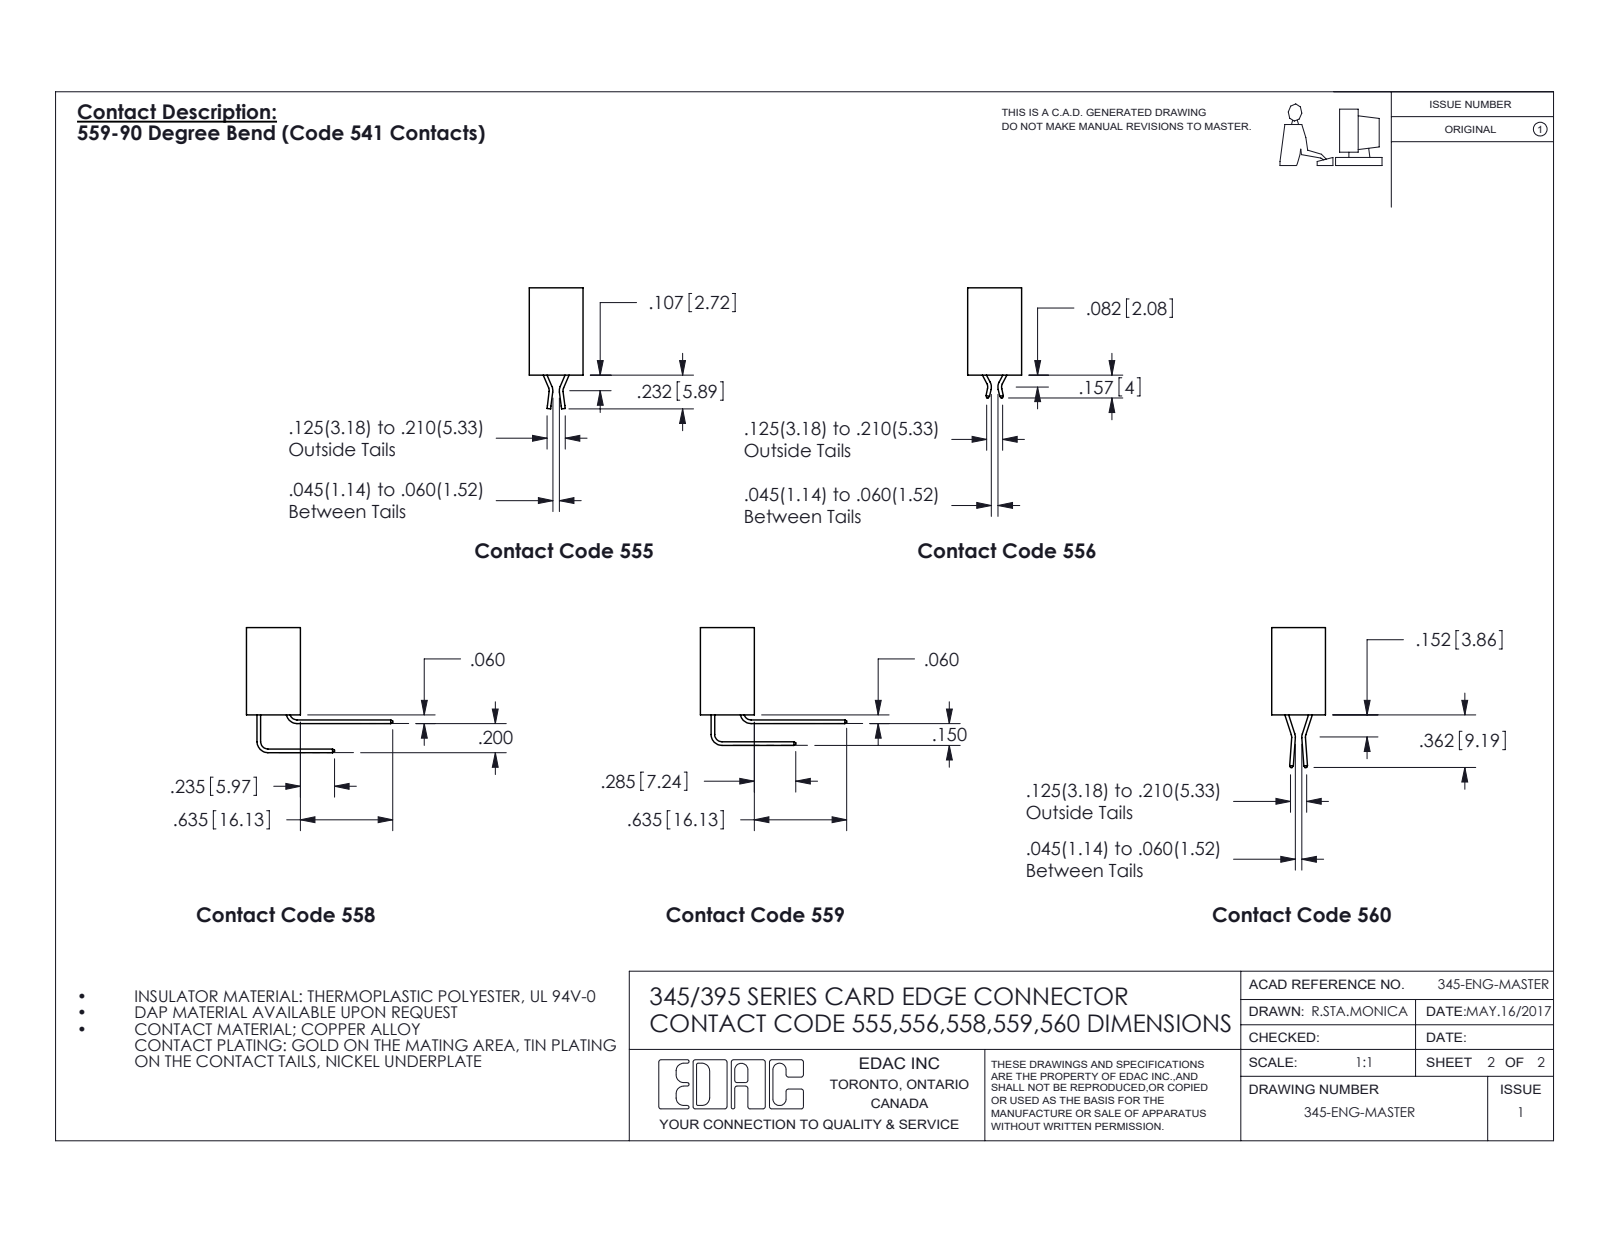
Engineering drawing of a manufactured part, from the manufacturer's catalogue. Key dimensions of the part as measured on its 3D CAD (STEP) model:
Part name (STEP PRODUCT): 345 Part_No Mounting Lugs; 345-020-555-201; 345-292-001_555 Tail
STEP written by: SolidWorks 2016 (CONFIG_CONTROL_DESIGN)
Units: inches
Bodies: 21 solids, 1238 faces (696 planar, 542 cylindrical, 0 other)
Overall size (bounding box): 1.26 × 0.832 × 0.37
Volume: 0.213 in³ · Surface area: 7.809 in²
Round holes (diameter × count): ⌀0.064 ×1
Partial cylindrical surfaces — rounded edges, fillets, slot ends (radius × count): R0.016 ×50, R0.02 ×40, R0.006 ×30, R0.01 ×22, R0.007 ×6, R0.031 ×6, R0.026 ×3, R0.01 ×2
Main face-to-face distances: 0.2, 0.298, 0.072, 0.1, 0.37, 0.025, 0.6, 0.098, 0.272, 0.3
